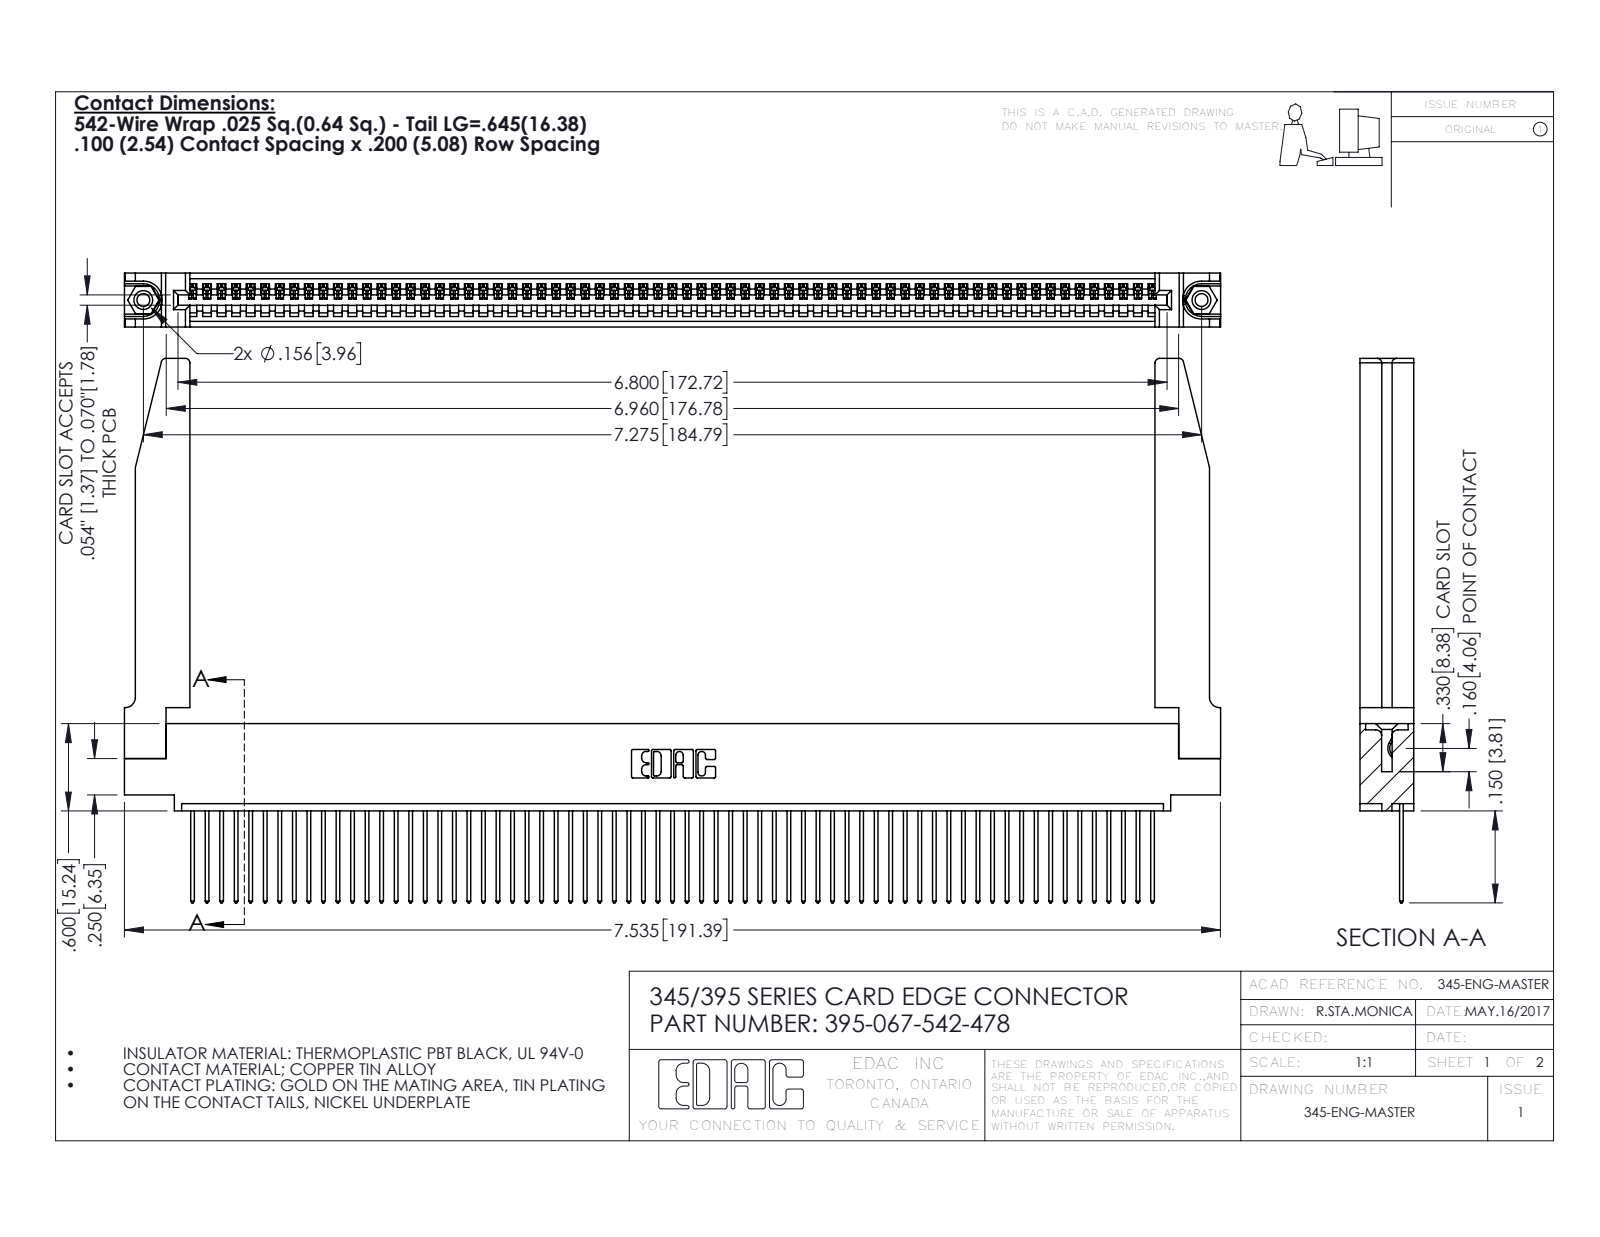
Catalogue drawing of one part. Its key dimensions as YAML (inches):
part_name: "345-220-078_345-220-078; 345-292-001_345-293-142; 345 Part_0.110 Offset - 0.156 Dia-TH; 345-250-001_345-250-001-102 (+1 more)"
step_written_by: "SolidWorks 2016 (CONFIG_CONTROL_DESIGN)"
units: inches
bodies: {solids: 72, faces: 4250, planar: 2906, cylindrical: 1292, other: 52}
overall_size: [7.536, 3.742, 0.37]
volume: 1.601
surface_area: 50.75
round_holes:
  - {diameter: 0.089, count: 2}
  - {diameter: 0.125, count: 2}
  - {diameter: 0.156, count: 2}
  - {diameter: 0.064, count: 1}
round_bosses_or_shafts:
  - {diameter: 0.155, count: 2}
partial_cylinders:
  - {radius: 0.006, count: 134}
  - {radius: 0.01, count: 134}
  - {radius: 0.01, count: 22}
  - {radius: 0.03, count: 8}
  - {radius: 0.007, count: 6}
  - {radius: 0.031, count: 6}
  - {radius: 0.026, count: 3}
  - {radius: 0.031, count: 2}
face_to_face_distances: [0.072, 0.298, 0.37, 0.098, 0.272, 0.025, 0.2, 0.225, 0.149, 0.148]
hole_center_spacings: [0.27, 7.039, 7.275]
